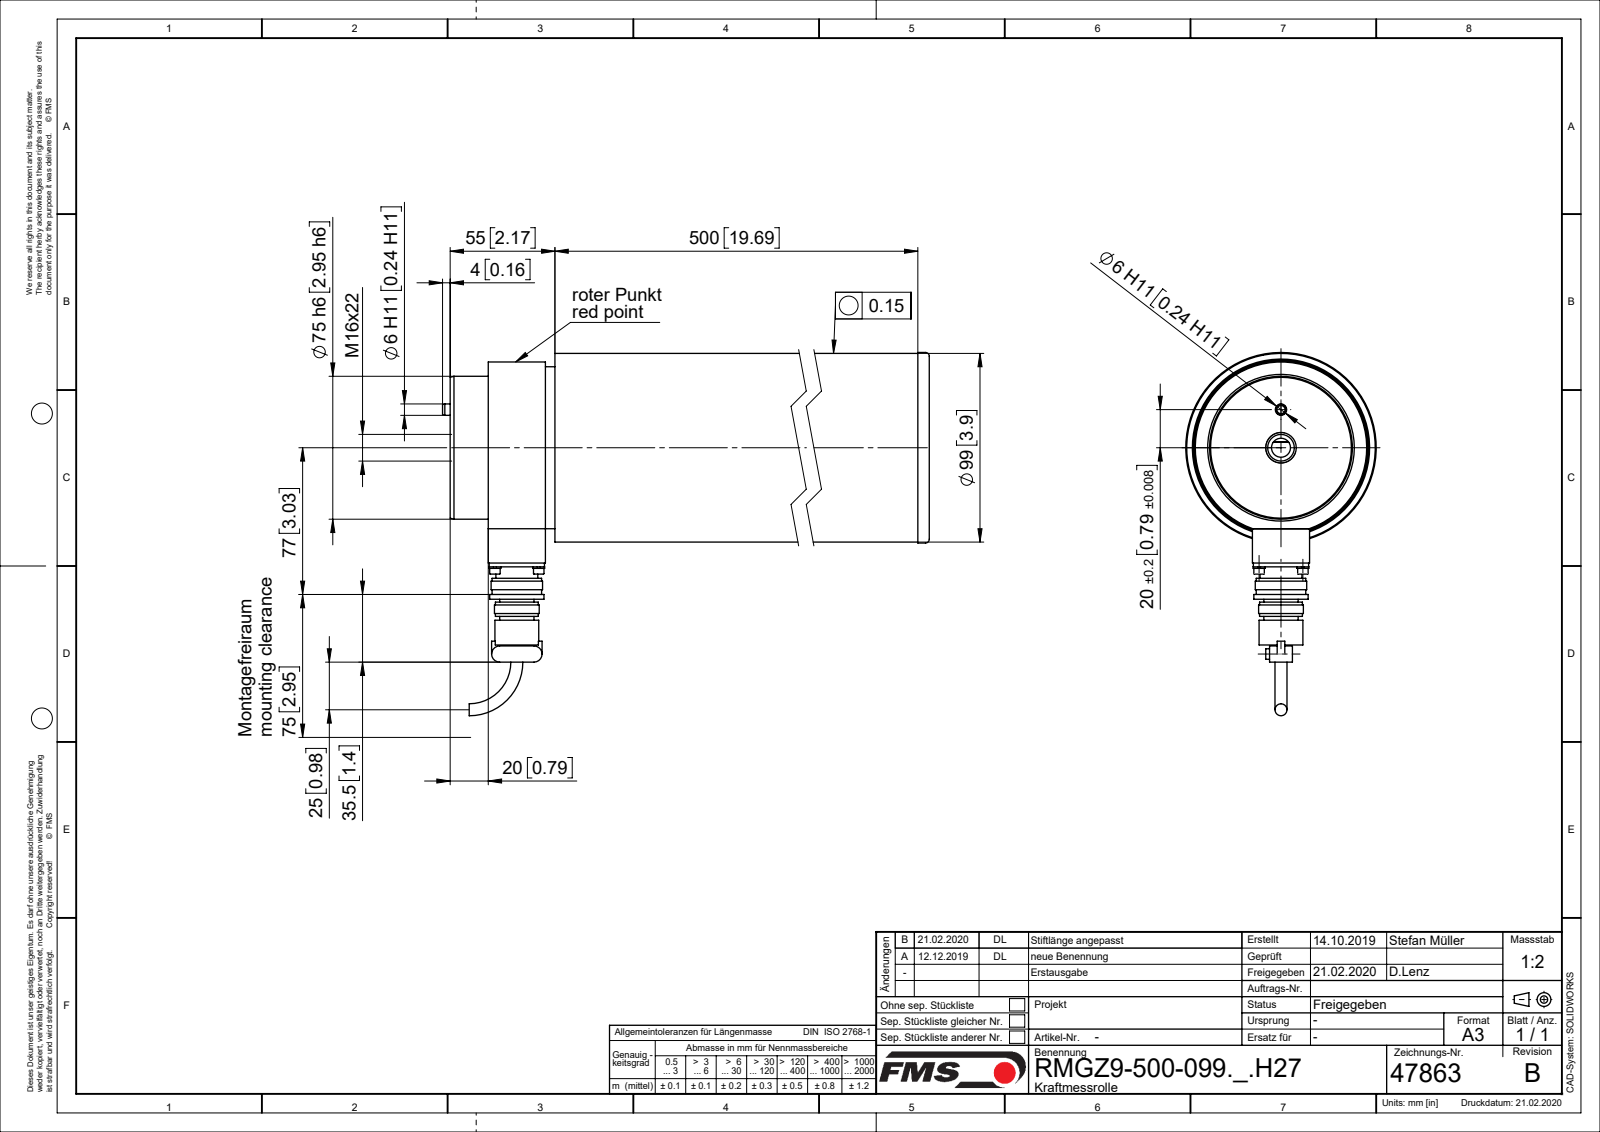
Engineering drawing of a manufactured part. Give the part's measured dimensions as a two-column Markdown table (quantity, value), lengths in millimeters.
| quantity | value |
| --- | --- |
| part name | 47868_H15; 47863_stp; 47849_01; Spannstift_ISO13337_D06x12 (+8 more) |
| STEP written by | SolidWorks 2018 (CONFIG_CONTROL_DESIGN) |
| units | millimeters |
| bodies | 31 solids, 570 faces (162 planar, 234 cylindrical, 174 other) |
| overall size | 565 × 190.65 × 100 |
| volume | 1 736 000 mm³ |
| surface area | 532 973 mm² |
| round holes (diameter × count) | 2.5 × 4, 3.1 × 4, 3.4 × 4, 3.3 × 1, 5 × 1, 6 × 1, 10 × 1, 12 × 1, 14 × 1, 22 × 1, 23 × 1, 26 × 1 |
| round bosses / shafts (diameter × count) | 5.5 × 6, 6.2 × 4, 3 × 4, 2.5 × 4, 100 × 1, 99 × 1, 91 × 1, 90 × 1 |
| partial cylindrical surfaces (radius × count) | 11 × 4, 4.25 × 2, 17.5 × 1 |
| main face-to-face distances | 50, 156, 32, 188, 10, 160, 2, 35, 316, 349 |
| hole center spacings | 16.26, 23, 32.53, 20 |
